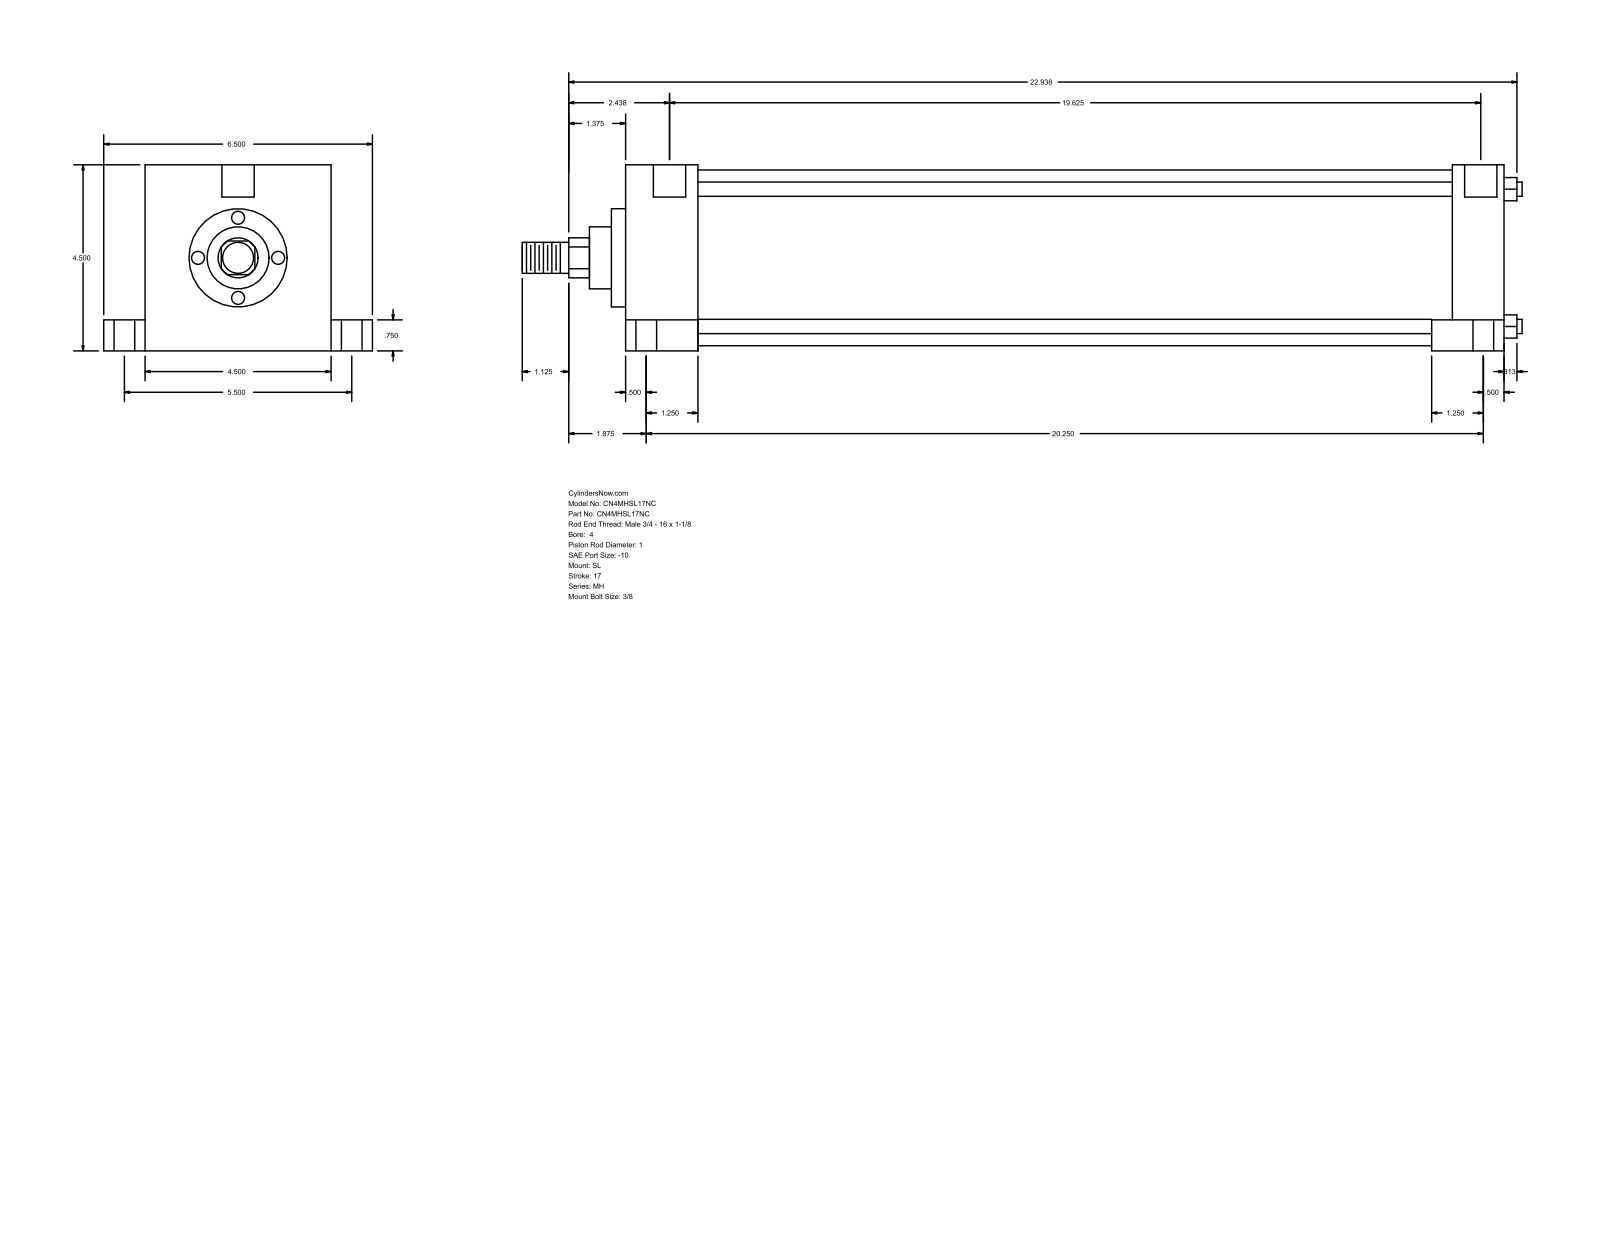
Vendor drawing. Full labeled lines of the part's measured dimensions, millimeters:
Part name (STEP PRODUCT): MH_SL__0400_1
STEP written by: GSSL Pune (CONFIG_CONTROL_DESIGN)
Units: millimetres
Bodies: 0 solids, 110 faces (77 planar, 33 cylindrical, 0 other)
Overall size (bounding box): 614.36 × 165.1 × 114.3
Round holes (diameter × count): ⌀8.73 ×4, ⌀12.7 ×4, ⌀19.05 ×4, ⌀19.84 ×2
Round bosses / shafts (diameter × count): ⌀8.76 ×4, ⌀107.95 ×1, ⌀60.33 ×1, ⌀38.1 ×1, ⌀25.4 ×1, ⌀19.05 ×1
Partial cylindrical surfaces — rounded edges, fillets, slot ends (radius × count): R12.29 ×1
Main face-to-face distances: 114.3, 539.75, 44.46, 495.29, 508, 463.54, 31.75, 25.4, 139.7, 19.05
Hole centre spacings: 69.85, 69.87, 71, 71.3, 139.7, 501.65, 504.92, 506.49
